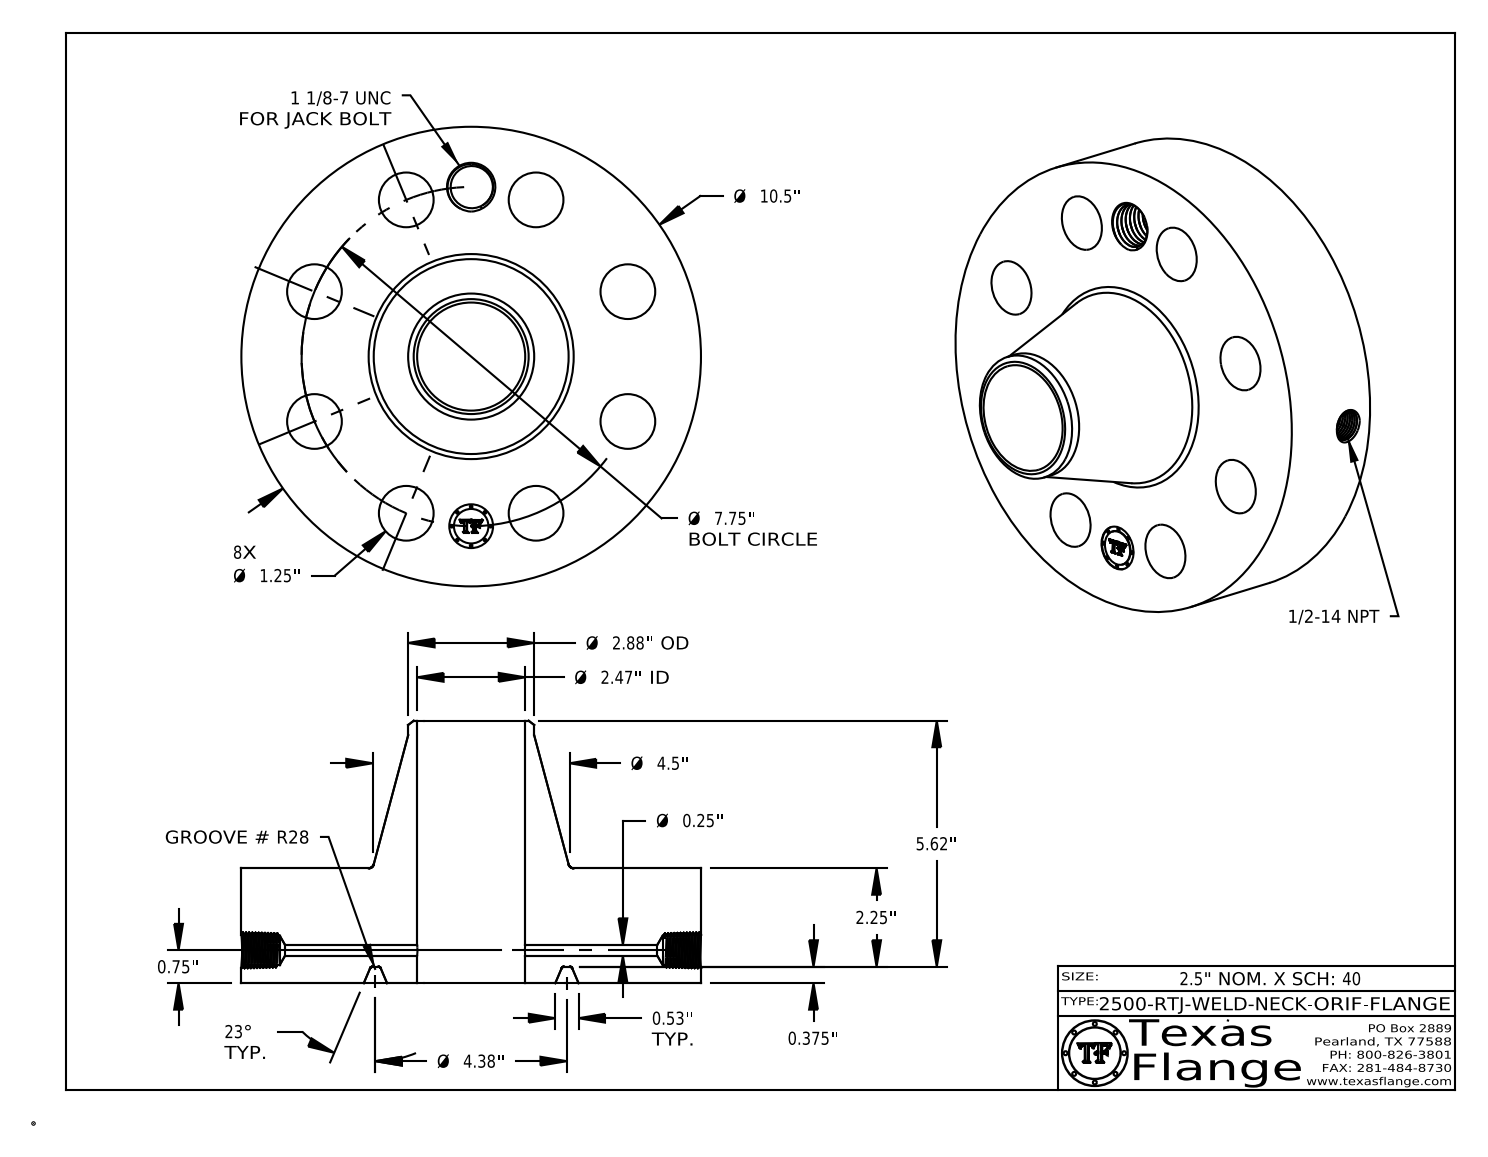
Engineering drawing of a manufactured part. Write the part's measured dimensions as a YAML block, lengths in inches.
part_name: "2500-RTJ-WELD-NECK"
step_written_by: "CATIA V5 STEP AP214 (AUTOMOTIVE_DESIGN)"
units: inches
bodies: {solids: 1, faces: 797, planar: 370, cylindrical: 98, other: 329}
overall_size: [10.5, 10.5, 5.995]
volume: 202.7
surface_area: 417.4
round_holes:
  - {diameter: 1.25, count: 8}
  - {diameter: 0.25, count: 1}
  - {diameter: 0.672, count: 1}
  - {diameter: 0.984, count: 1}
  - {diameter: 1, count: 1}
  - {diameter: 2.469, count: 1}
round_bosses_or_shafts:
  - {diameter: 0.061, count: 8}
  - {diameter: 10.5, count: 1}
  - {diameter: 2.88, count: 1}
  - {diameter: 0.788, count: 1}
face_to_face_distances: [2.625, 0.375, 2.25, 5.995, 5.62, 3.37, 2.61, 2.235, 0.015, 3.385]
hole_center_spacings: [3.875, 5.48, 1.512, 2.965, 2.966, 4.306, 6.444, 7.16]
